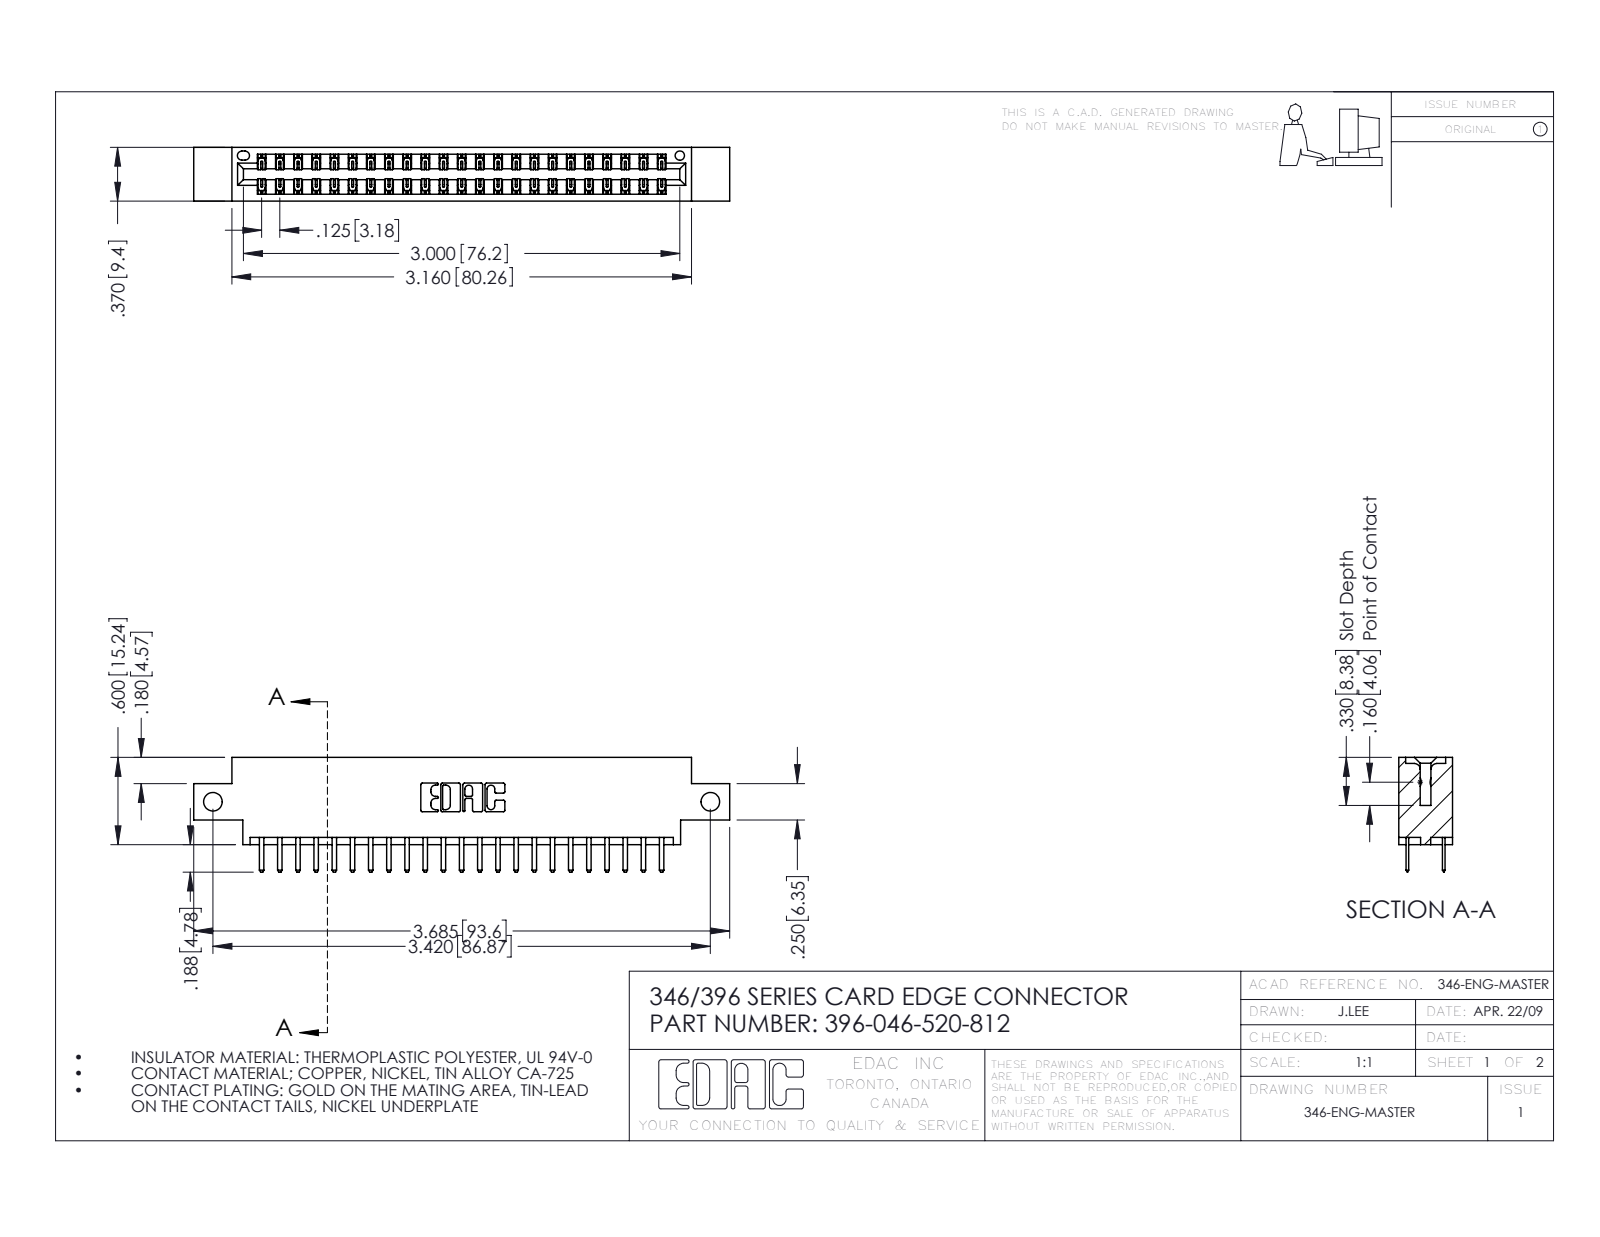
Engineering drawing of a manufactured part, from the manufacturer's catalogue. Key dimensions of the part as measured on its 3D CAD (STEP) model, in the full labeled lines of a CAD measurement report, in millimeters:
Part name (STEP PRODUCT): 396-046-520-812; 346 Part_0.170 Offset - Side Mount; 345-292-001_345-293-120
STEP written by: SolidWorks 2016 (CONFIG_CONTROL_DESIGN)
Units: millimetres
Bodies: 47 solids, 2702 faces (1782 planar, 920 cylindrical, 0 other)
Overall size (bounding box): 93.6 × 20 × 9.4
Volume: 8 720 mm³ · Surface area: 11 680 mm²
Round holes (diameter × count): ⌀3.3 ×2, ⌀1.6 ×1
Partial cylindrical surfaces — rounded edges, fillets, slot ends (radius × count): R0.2 ×69, R0.3 ×50, R0.3 ×22, R0.2 ×6, R0.8 ×6, R0.7 ×3, R0.4 ×2, R0.6 ×2
Main face-to-face distances: 1.2, 8.2, 6.4, 9.4, 7, 1.8, 7.6, 0.6, 3.8, 5.6
Hole centre spacings: 86.9
